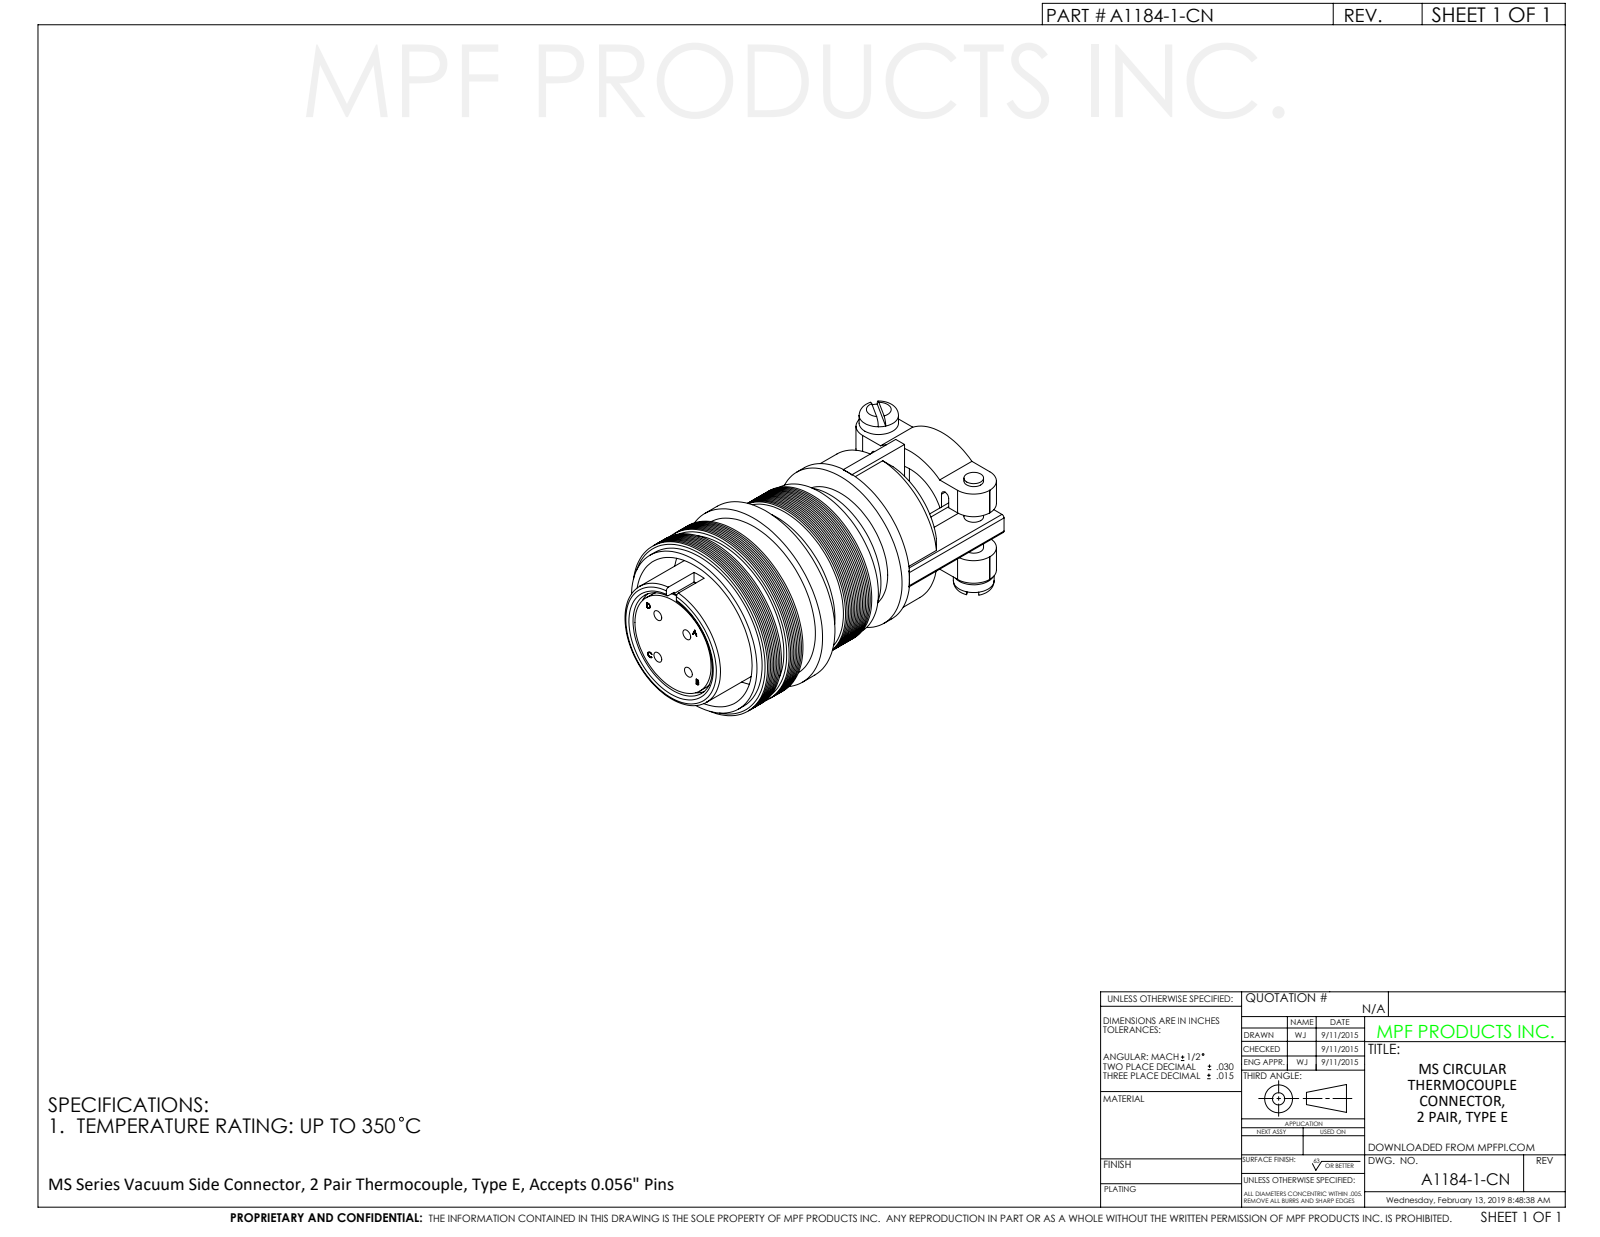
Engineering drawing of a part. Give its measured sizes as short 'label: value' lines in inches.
name: A1070-2-CN
written by: SolidWorks 2012 (CONFIG_CONTROL_DESIGN)
unit: in
bodies: 1 solid, 376 faces (107 planar, 87 cylindrical, 182 other)
size: 2.737 × 1.34 × 1.34
volume: 2.274 in³; area: 25.21 in²
holes: 4× ⌀0.087, 1× ⌀0.55, 1× ⌀0.78, 1× ⌀1.125
bosses: 2× ⌀0.135, 1× ⌀1.34, 1× ⌀1.223, 1× ⌀1.22, 1× ⌀1.2, 1× ⌀1.14, 1× ⌀0.99, 1× ⌀0.92
rounds: 8× R0.034, 4× R0.02, 4× R0.156, 1× R0.323, 1× R0.472, 1× R0.473
face distances: 1.193, 0.1, 0.643, 0.47, 0.722, 1.714, 0.2, 2.096, 1.626, 0.904
hole spacings: 0.19, 0.269, 0.38
